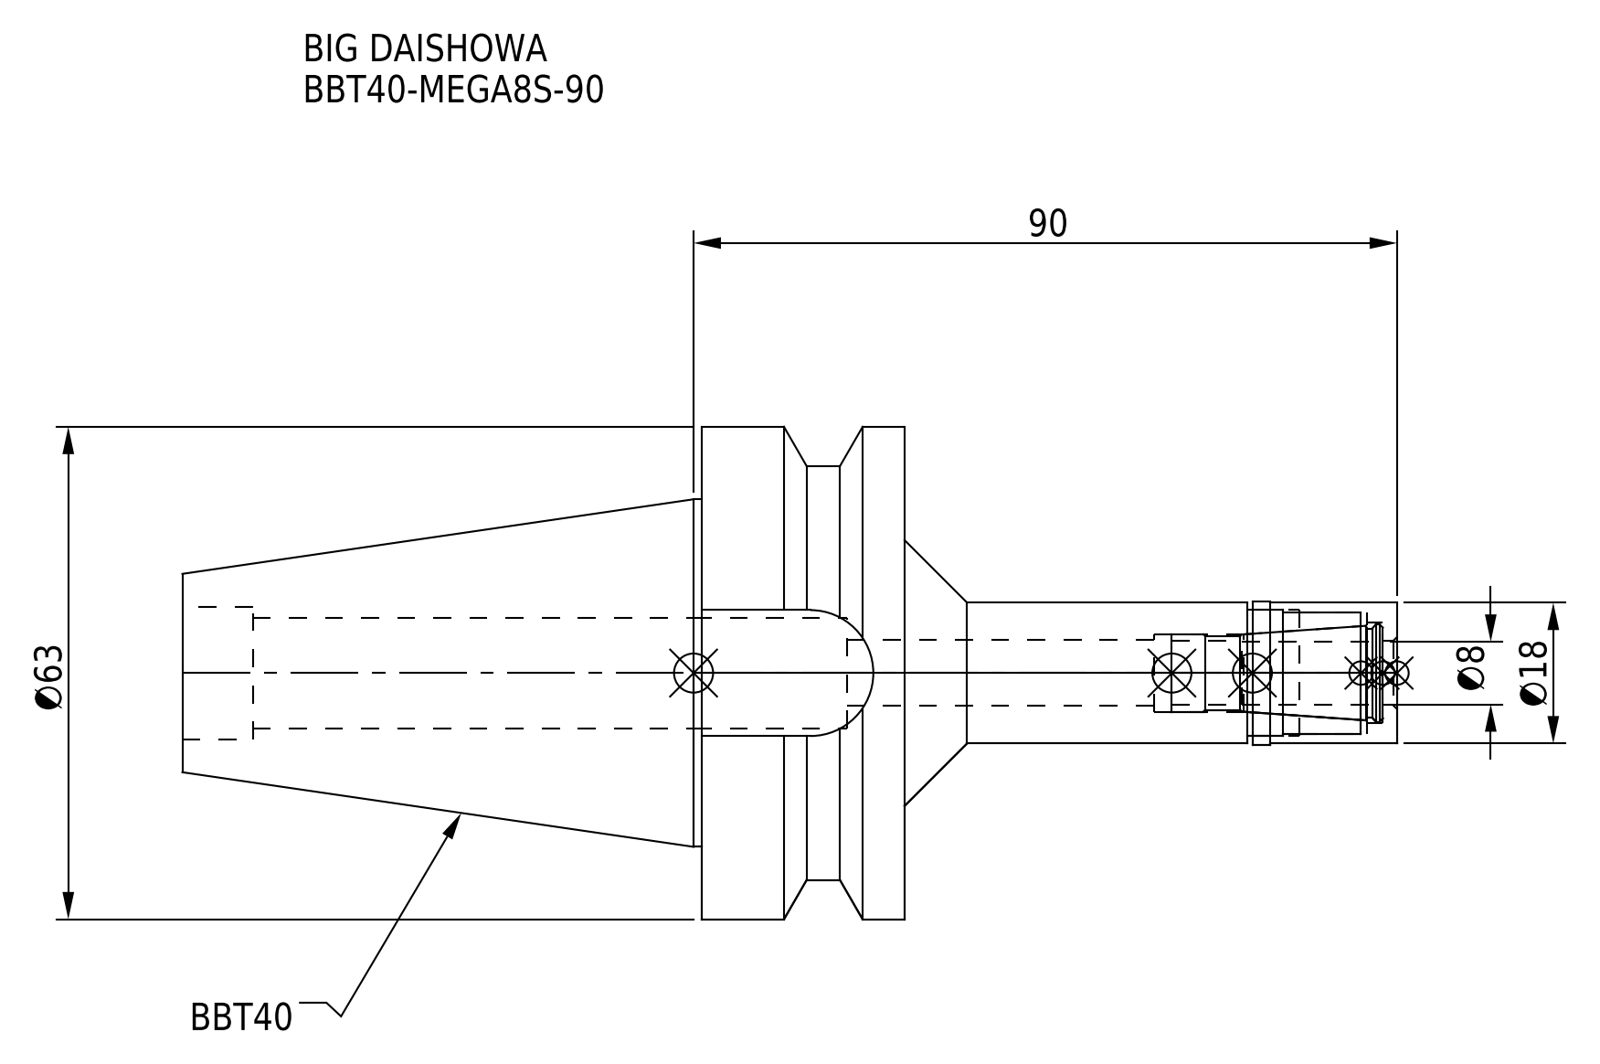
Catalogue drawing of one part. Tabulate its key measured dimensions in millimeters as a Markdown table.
| quantity | value |
| --- | --- |
| part name | BBT40-MEGA8S-90_1.stp; BBT40-MEGA8S-90-080.stp; BBT40-MEGA8S-90-080-FreeParts; MGN8S_1.stp (+3 more) |
| STEP written by | SolidWorks 2019 (CONFIG_CONTROL_DESIGN) |
| units | millimeters |
| bodies | 2 solids, 71 faces (21 planar, 38 cylindrical, 12 other) |
| overall size | 155.4 × 63 × 63 |
| volume | 134 848 mm³ |
| surface area | 29 785 mm² |
| round holes (diameter × count) | 8.2 × 1, 8.4 × 1, 9.9 × 1, 12.9 × 1, 14.2 × 1, 15.6 × 1, 16.1 × 1, 17 × 1 |
| round bosses / shafts (diameter × count) | 63 × 1, 53 × 1, 44.45 × 1, 18.3 × 1, 18 × 1 |
| partial cylindrical surfaces (radius × count) | 8.05 × 1 |
| main face-to-face distances | 26, 45, 92.4, 66.4, 16.1, 63, 89, 155.4, 18.6, 70.4 |
